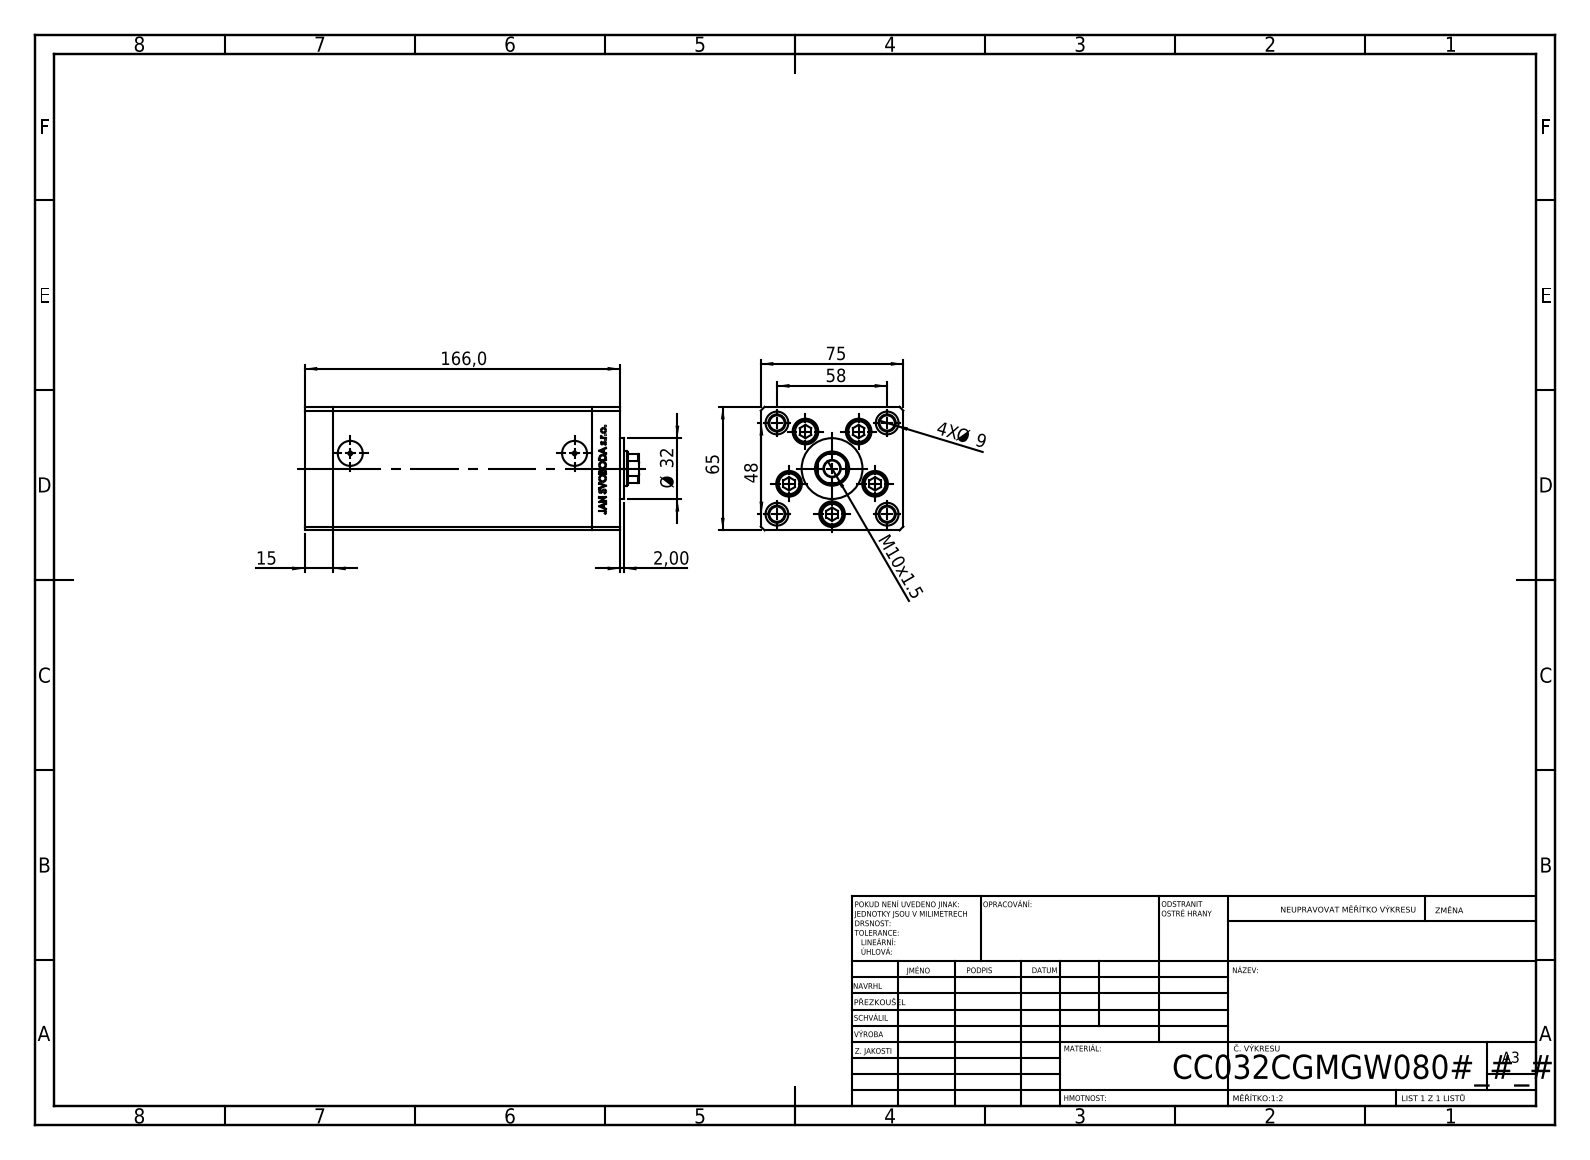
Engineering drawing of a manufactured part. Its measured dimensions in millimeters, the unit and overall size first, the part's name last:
Units: millimetres
Overall size (bounding box): 176 × 75 × 65
Round holes (diameter × count): ⌀9 ×9, ⌀13.5 ×5, ⌀8 ×4, ⌀12 ×4, ⌀2 ×2, ⌀13.16 ×2, ⌀8.5 ×1, ⌀12.5 ×1, ⌀18 ×1
Round bosses / shafts (diameter × count): ⌀8 ×5, ⌀12.5 ×4, ⌀32 ×1
Partial cylindrical surfaces — rounded edges, fillets, slot ends (radius × count): R0.93 ×2, R8.5 ×1
Main face-to-face distances: 75, 65, 15, 136, 151, 166, 28, 142, 13, 9
Hole centre spacings: 24, 37.64, 15.67, 17.22, 27.71, 28.83, 29, 32.63
Volume: 680 499 mm³ · Surface area: 142 517 mm²
Bodies: 13 solids, 1169 faces (540 planar, 167 cylindrical, 462 other)
Part name (STEP PRODUCT): V220C BACK_C; V220C_C MIDDLE; V220C_VC_C; V220C FRONT (+1 more)
STEP written by: SolidWorks 2019 (CONFIG_CONTROL_DESIGN)
